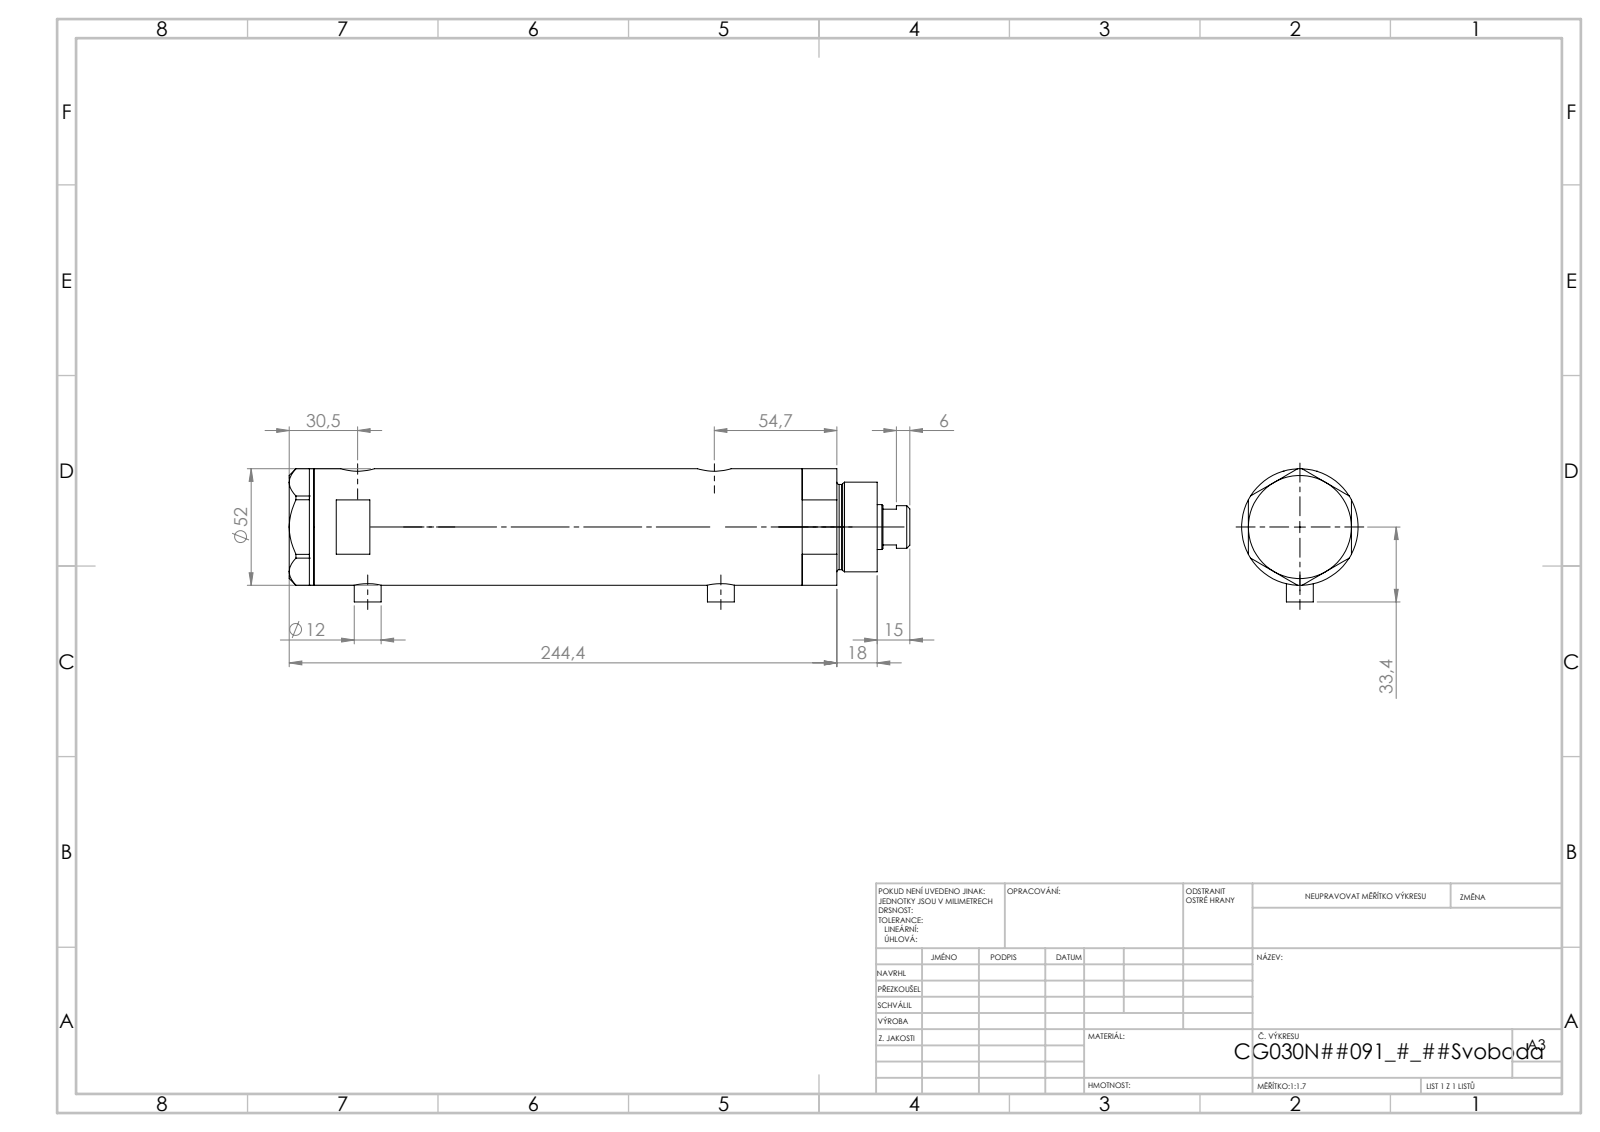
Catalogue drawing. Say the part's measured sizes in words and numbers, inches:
The part is named "V270CG_FRONT; V270CG_MIDDLE; V270CG_BACK; V270CG_VC". Its 3-D file was written by "SolidWorks 2019 (CONFIG_CONTROL_DESIGN)". It is 4 solids with 140 faces: 67 planar, 53 cylindrical and 20 other. Overall it measures 10.904 by 2.339 by 2.047 inches. Its volume is 30.65 cubic inches and its surface area 166.5 square inches. Round holes: 2 of diameter 0.197, 2 of diameter 0.383, 2 of diameter 0.492, 2 of diameter 0.591, 1 of diameter 0.256, 1 of diameter 0.787, 1 of diameter 0.846, 1 of diameter 1.181, 1 of diameter 1.299, 1 of diameter 1.732. Round bosses or shafts: 2 of diameter 0.472, 1 of diameter 2.047, 1 of diameter 1.575, 1 of diameter 1.496, 1 of diameter 0.748. The main face-to-face distances are 7.146, 0.937, 6.209, 0.433, 1.37, 7.579, 1.811, 9.012, 8.579, 7.642. The hole center spacings are 0.114, 0.177, 6.091, 6.205, 6.268, 6.382.
